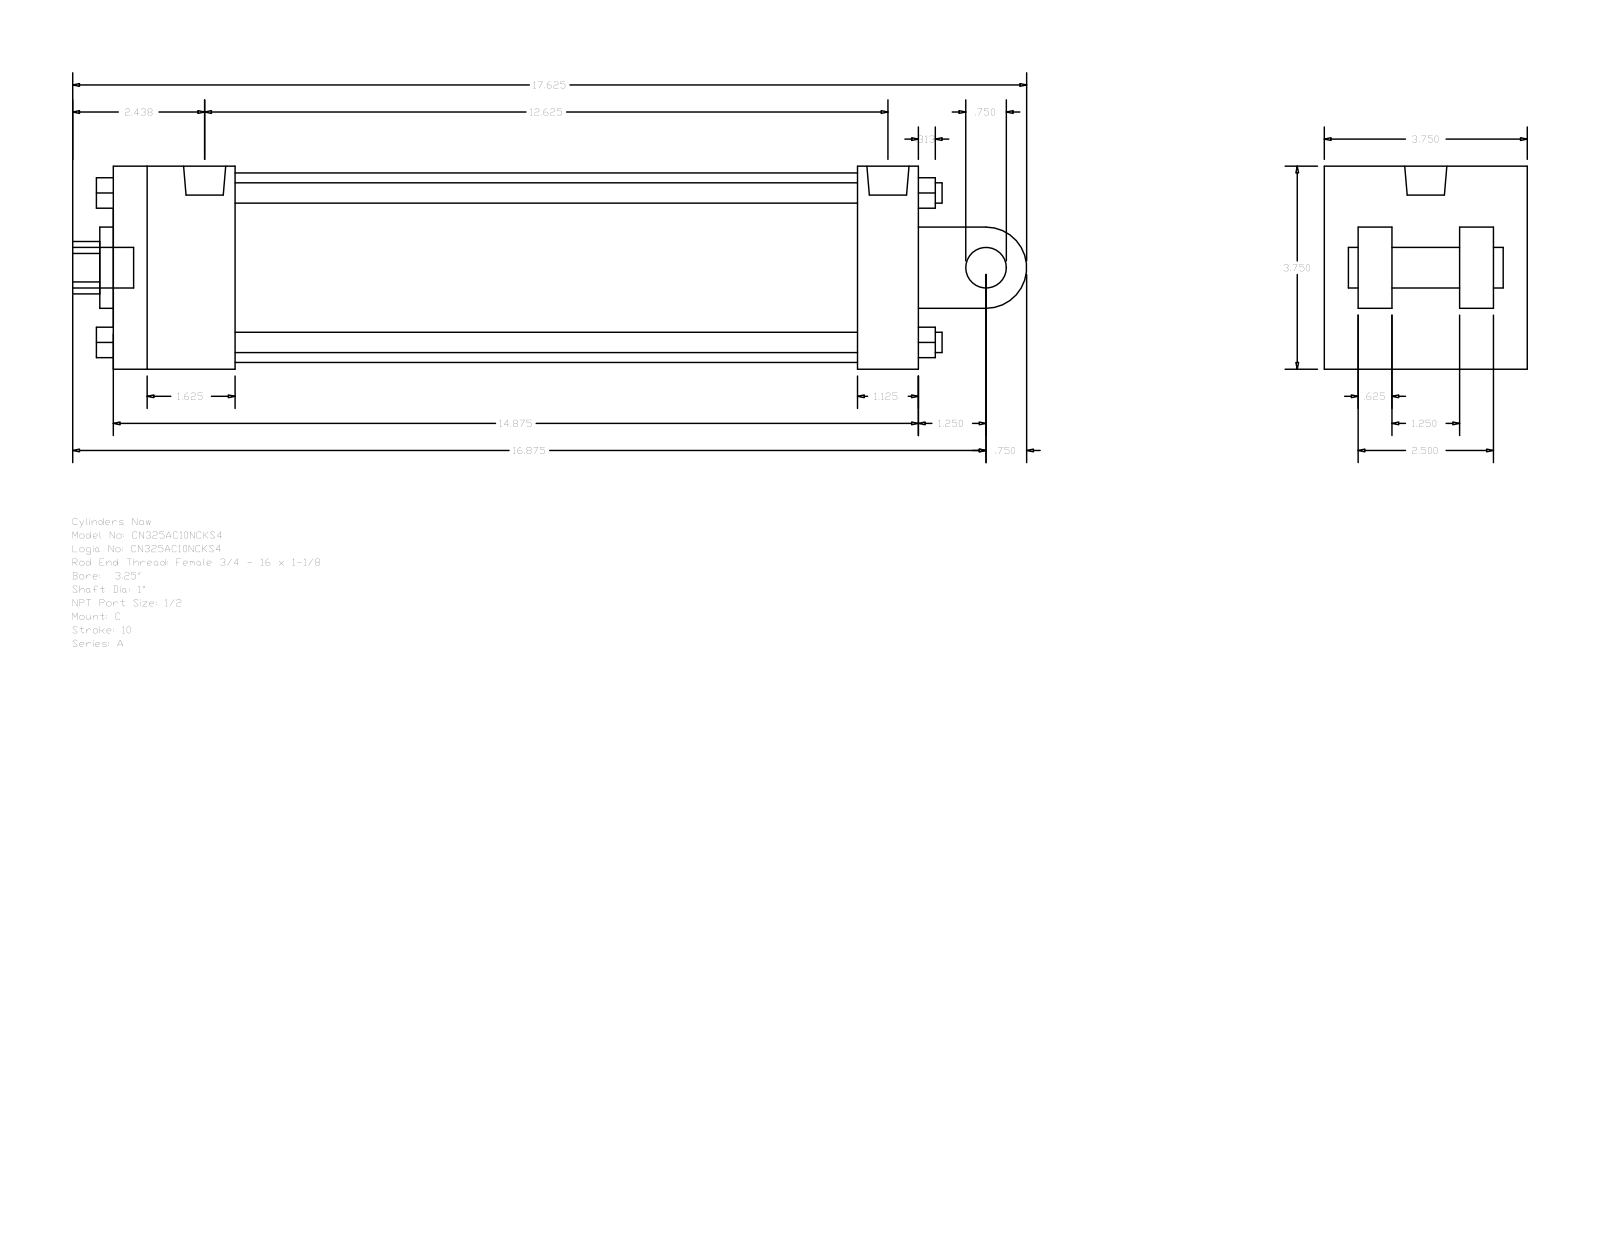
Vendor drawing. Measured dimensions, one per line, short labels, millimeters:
name: A_C__0325_1
written by: GSSL Pune (CONFIG_CONTROL_DESIGN)
unit: mm
bodies: 0 solids, 135 faces (102 planar, 33 cylindrical, 0 other)
size: 447.68 × 95.25 × 95.25
holes: 2× ⌀8.73, 1× ⌀19.77, 1× ⌀25.4, 1× ⌀38.1, 1× ⌀88.9
bosses: 4× ⌀9.53, 2× ⌀19.05, 2× ⌀8.73, 1× ⌀19.77
rounds: 1× R12.29, 1× R19.05
face distances: 95.24, 377.83, 15.87, 63.5, 47.63, 79.37, 31.74, 66.67, 349.25, 28.58
hole spacings: 3.18
